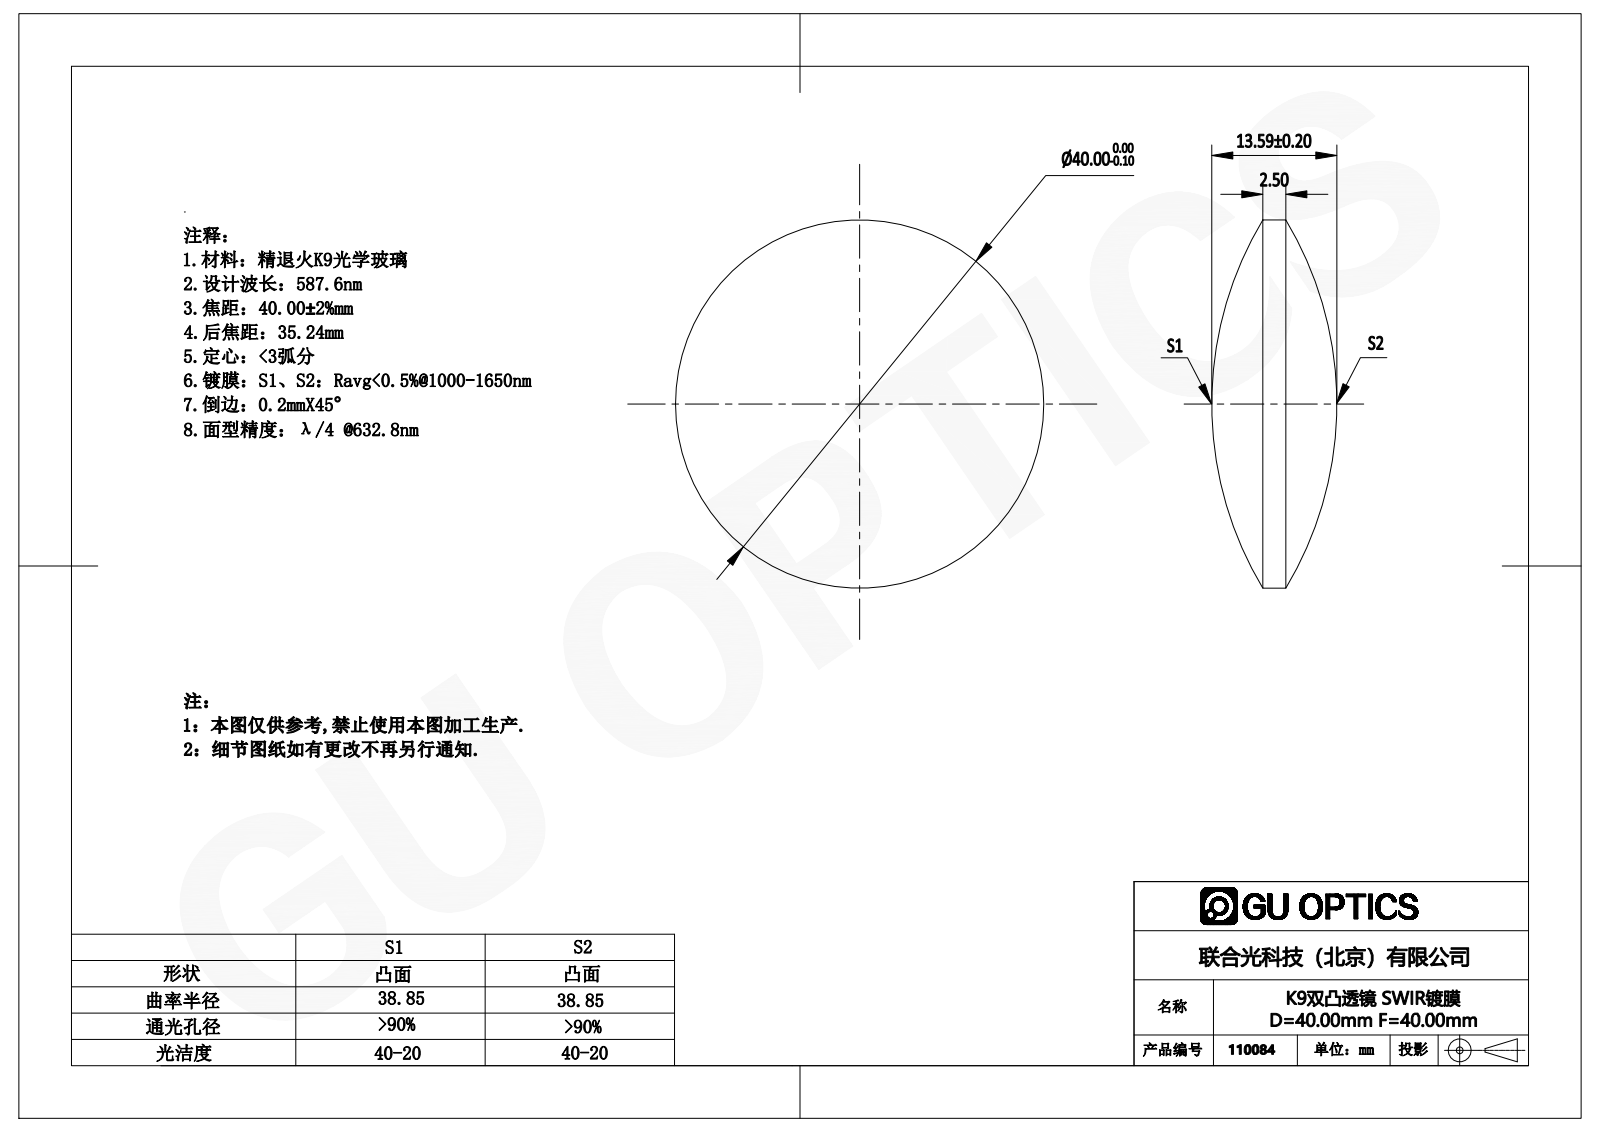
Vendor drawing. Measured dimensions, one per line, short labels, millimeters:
name: 110018
written by: SolidWorks 2016 (CONFIG_CONTROL_DESIGN)
unit: mm
bodies: 1 solid, 6 faces (0 planar, 2 cylindrical, 4 other)
size: 40 × 40 × 13.59
volume: 10 288 mm³; area: 3 021 mm²
bosses: 1× ⌀40
